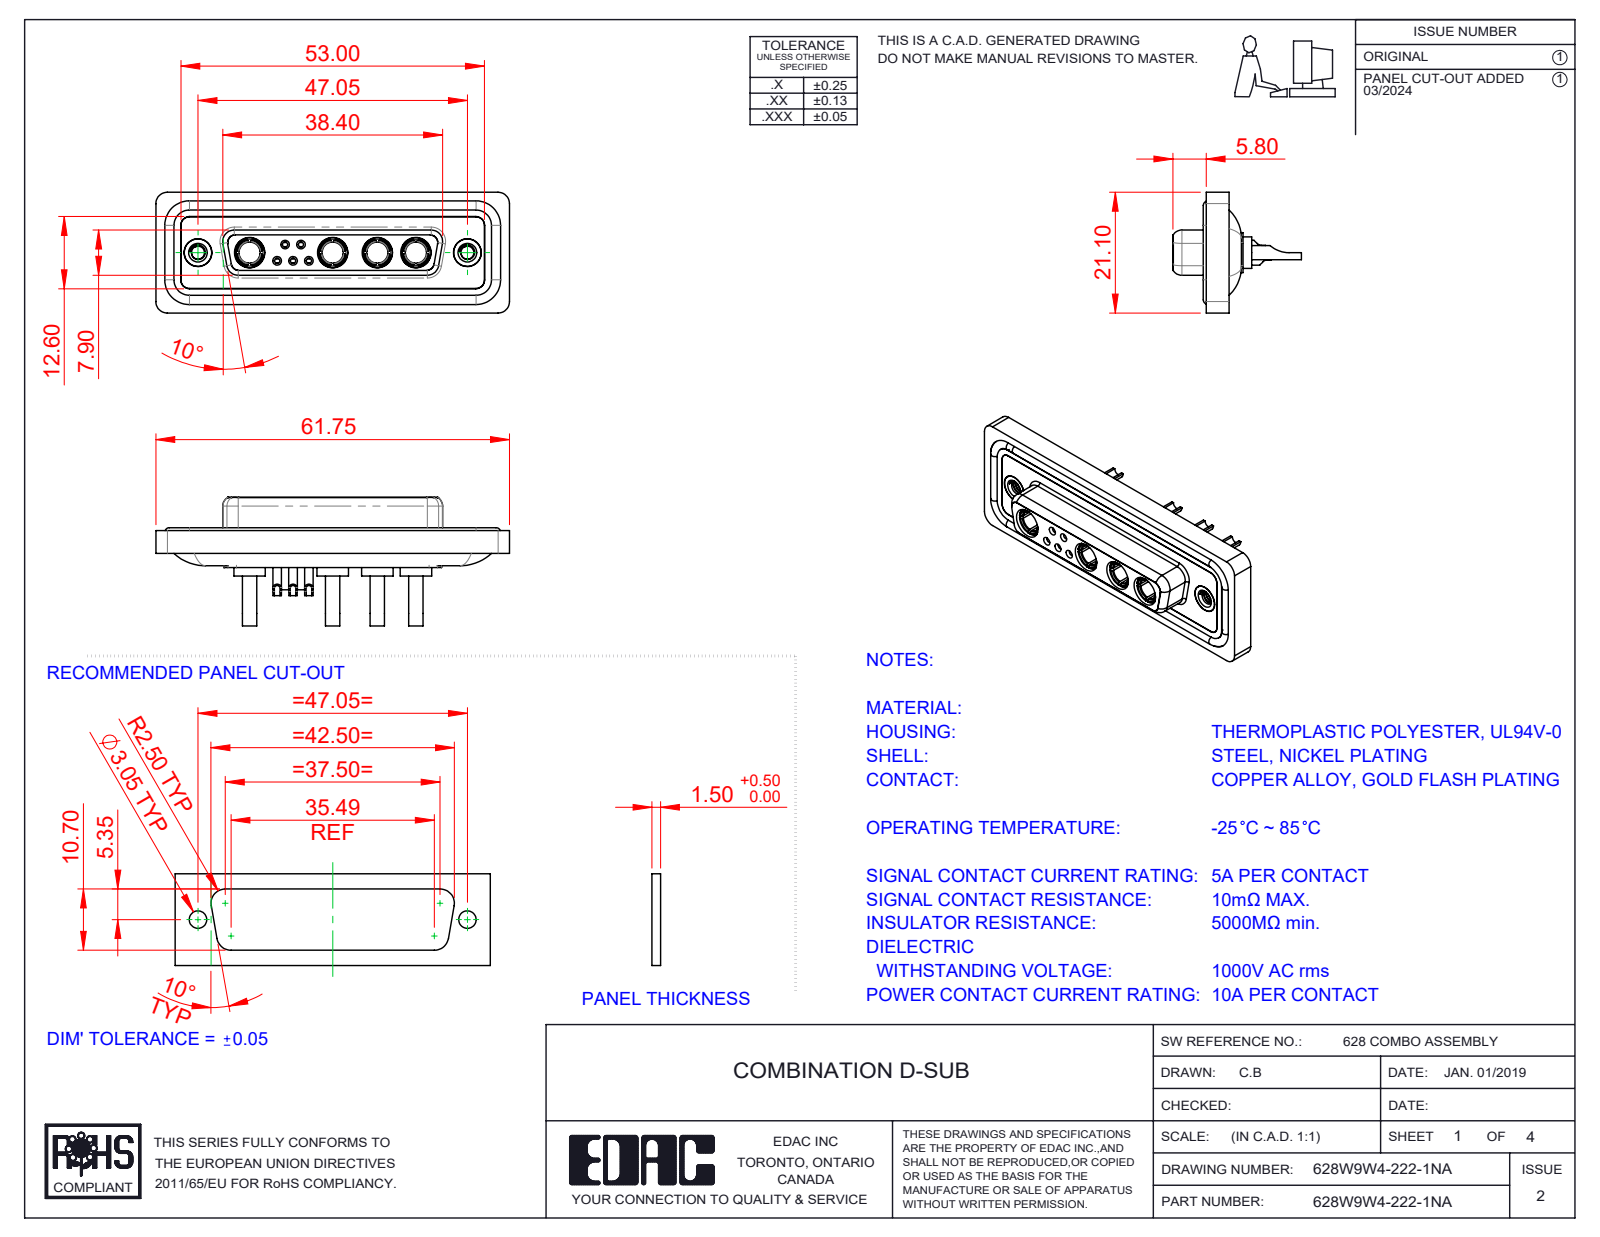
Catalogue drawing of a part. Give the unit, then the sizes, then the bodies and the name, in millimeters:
Units: millimetres
Overall size (bounding box): 61.75 × 22.45 × 21.1
Round holes (diameter × count): ⌀4.85 ×6, ⌀0.9 ×5, ⌀1 ×5, ⌀1.1 ×5, ⌀1.5 ×5, ⌀2 ×5, ⌀1.7 ×4, ⌀3.7 ×4, ⌀5.3 ×4, ⌀1.6 ×3, ⌀1.7 ×2, ⌀2.26 ×2
Round bosses / shafts (diameter × count): ⌀1.6 ×6, ⌀2.2 ×5, ⌀5.5 ×4, ⌀5.2 ×4, ⌀4.96 ×4, ⌀4.75 ×4, ⌀3.75 ×4, ⌀2.5 ×4
Partial cylindrical surfaces — rounded edges, fillets, slot ends (radius × count): R1.5 ×22, R2 ×18, R1.35 ×8, R1.6 ×8, R1 ×6, R0.25 ×4, R0.5 ×4, R0.6 ×4
Main face-to-face distances: 0.4, 1.8, 7.45, 5.65, 0.5, 7.05, 6.6, 1.6, 1.1, 2.9
Hole centre spacings: 3.16, 2.77, 5.03, 2.76, 4.4, 5.02, 5.54, 5.73
Volume: 8 225 mm³ · Surface area: 13 805 mm²
Bodies: 20 solids, 975 faces (314 planar, 399 cylindrical, 262 other)
Part name (STEP PRODUCT): 628Combo Waterproof Housing_25 Contacts; 628Combo Threaded Rivet_A; 628W9W4-222-1NA; 628Combo Shell Front_25 Contacts (+5 more)
STEP written by: SolidWorks 2023 (CONFIG_CONTROL_DESIGN)
